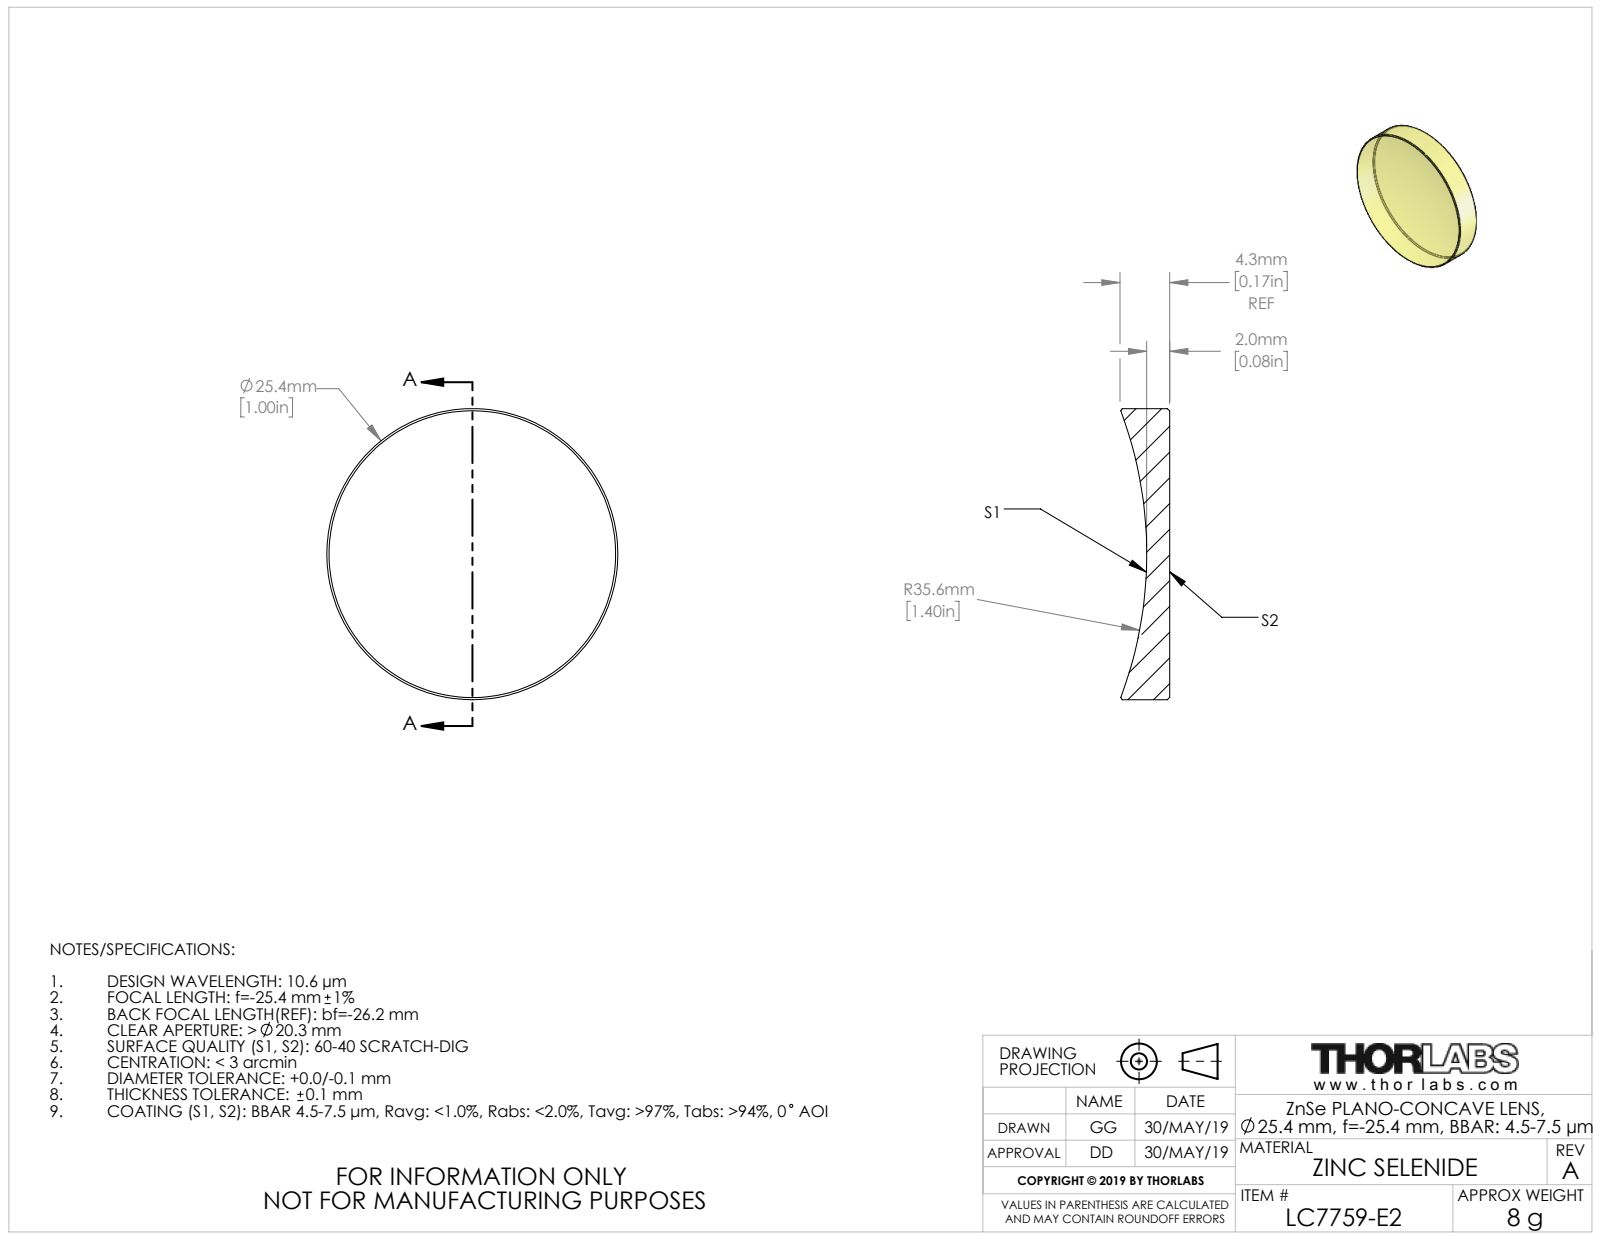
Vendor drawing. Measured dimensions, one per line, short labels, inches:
name: TTN047636-E0W
written by: SolidWorks 2018 (CONFIG_CONTROL_DESIGN)
unit: in
bodies: 1 solid, 9 faces (1 planar, 2 cylindrical, 6 other)
size: 1 × 1 × 0.168
volume: 0.097 in³; area: 2.099 in²
bosses: 1× ⌀1
